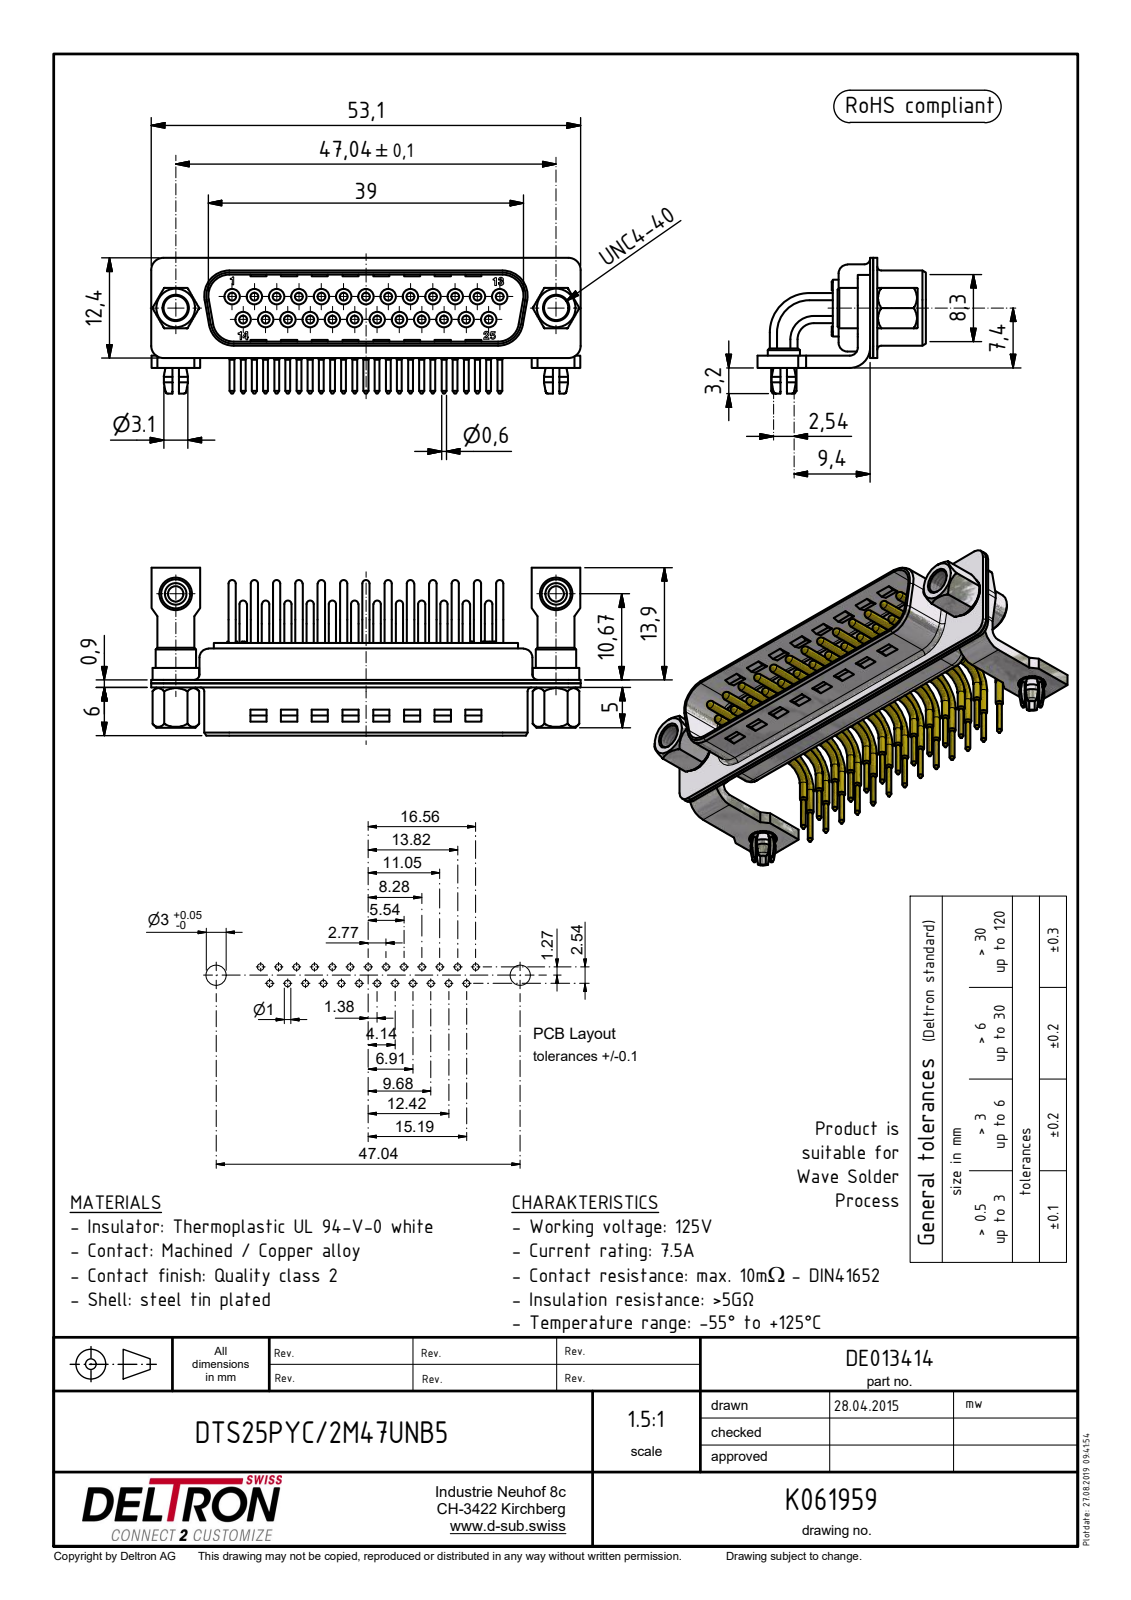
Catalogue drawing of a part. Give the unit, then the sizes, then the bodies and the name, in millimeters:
Units: millimetres
Overall size (bounding box): 53.1 × 20.8 × 16.8
Round holes (diameter × count): ⌀1.92 ×25, ⌀2.3 ×25, ⌀0.34 ×2, ⌀1.9 ×2, ⌀3 ×2, ⌀3.2 ×2, ⌀3.4 ×2, ⌀4.05 ×2, ⌀4.06 ×2
Round bosses / shafts (diameter × count): ⌀0.9 ×50, ⌀1.96 ×25, ⌀1.94 ×25, ⌀1.6 ×25, ⌀1.6 ×25, ⌀1 ×25, ⌀0.6 ×25, ⌀4 ×4
Partial cylindrical surfaces — rounded edges, fillets, slot ends (radius × count): R1.07 ×25, R2 ×20, R1 ×9, R0.5 ×8, R0.7 ×8, R1.1 ×8, R0.25 ×6, R1.2 ×4
Main face-to-face distances: 0.5, 0.4, 0.65, 8.8, 0.9, 10.05, 1.25, 1.5, 5, 2.4
Hole centre spacings: 3.16, 2.76, 5.02, 5.52, 7.46, 8.28, 10.07, 11.04
Volume: 3 203 mm³ · Surface area: 8 881 mm²
Bodies: 36 solids, 4154 faces (2536 planar, 1326 cylindrical, 292 other)
Part name (STEP PRODUCT): N00405_kleine_Datei_BG; R+B00913_BG; R+B00914_BG; R+B00128_BG (+6 more)
STEP written by: Autodesk Inventor 2015 (AUTOMOTIVE_DESIGN)
